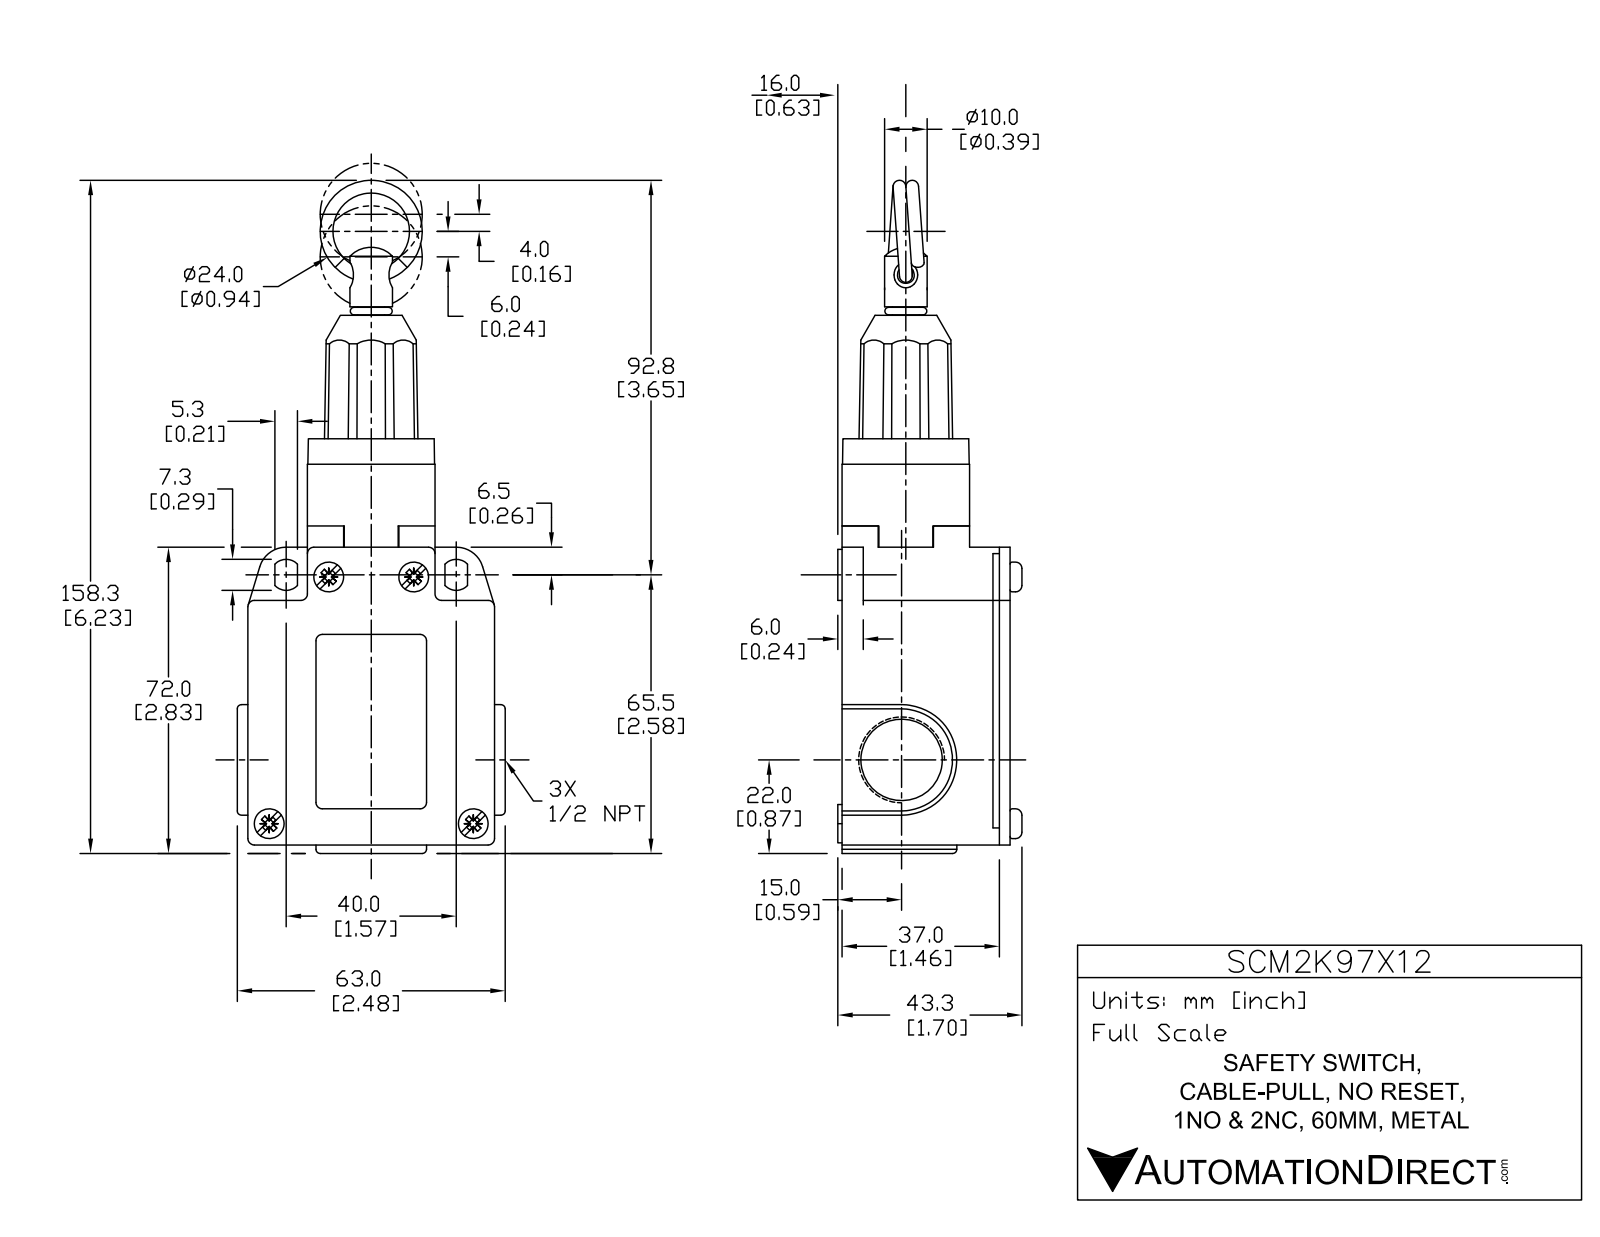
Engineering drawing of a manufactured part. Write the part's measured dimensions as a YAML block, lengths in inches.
part_name: "SCM2K97X12"
step_written_by: "SolidWorks 2017 (AUTOMOTIVE_DESIGN)"
units: inches
bodies: {solids: 5, faces: 202, planar: 89, cylindrical: 88, other: 25}
overall_size: [6.28, 2.441, 1.705]
volume: 10.97
surface_area: 48.85
round_holes:
  - {diameter: 0.669, count: 2}
  - {diameter: 0.748, count: 2}
  - {diameter: 0.157, count: 1}
  - {diameter: 0.398, count: 1}
  - {diameter: 0.709, count: 1}
round_bosses_or_shafts:
  - {diameter: 0.276, count: 4}
  - {diameter: 0.472, count: 2}
  - {diameter: 0.354, count: 2}
  - {diameter: 0.701, count: 1}
  - {diameter: 0.394, count: 1}
  - {diameter: 0.248, count: 1}
partial_cylinders:
  - {radius: 0.059, count: 12}
  - {radius: 0.144, count: 2}
  - {radius: 0.256, count: 2}
  - {radius: 0.512, count: 2}
  - {radius: 0.453, count: 1}
  - {radius: 0.472, count: 1}
face_to_face_distances: [1.555, 0.551, 1.732, 1.181, 2.283, 0.079, 0.236, 0.157, 0.197, 2.756]
hole_center_spacings: [0.039, 4.528]
